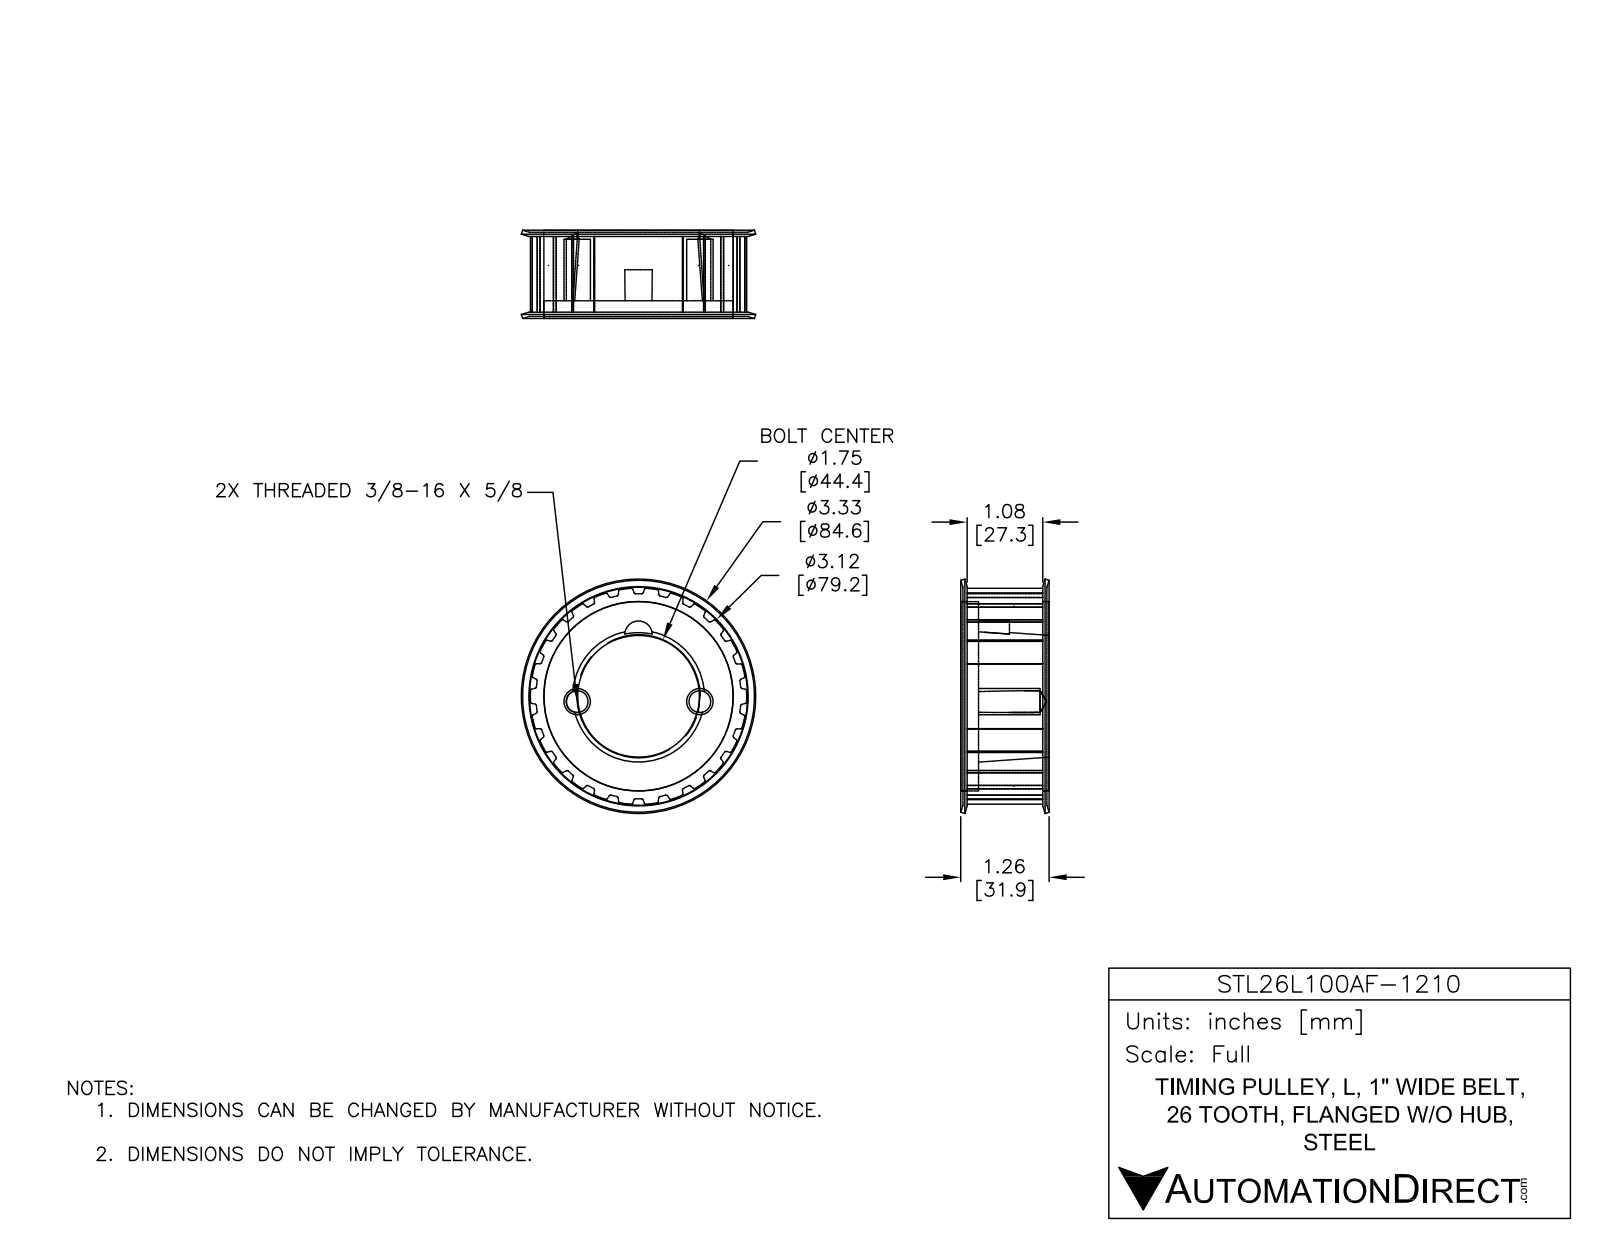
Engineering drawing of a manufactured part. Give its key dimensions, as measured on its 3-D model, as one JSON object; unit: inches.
{"part_name": "STL26L100AF-1210", "step_written_by": "SolidWorks 2018 (AUTOMOTIVE_DESIGN)", "units": "inches", "bodies": {"solids": 1, "faces": 271, "planar": 88, "cylindrical": 165, "other": 18}, "overall_size": [3.33, 3.33, 1.168], "volume_in3": 5.107, "surface_area_in2": 38.33, "round_holes": [[2.187, 1], [2.692, 1]], "round_bosses_or_shafts": [[2.689, 1]], "partial_cylinders_radius": [[0.015, 52], [0.02, 52], [0.155, 2], [0.195, 1], [1.537, 1]], "face_to_face_distances": [1.163, 0.027, 1.135, 1.108, 1.135, 0.028, 0.087, 1.075, 0.19, 0.163]}
